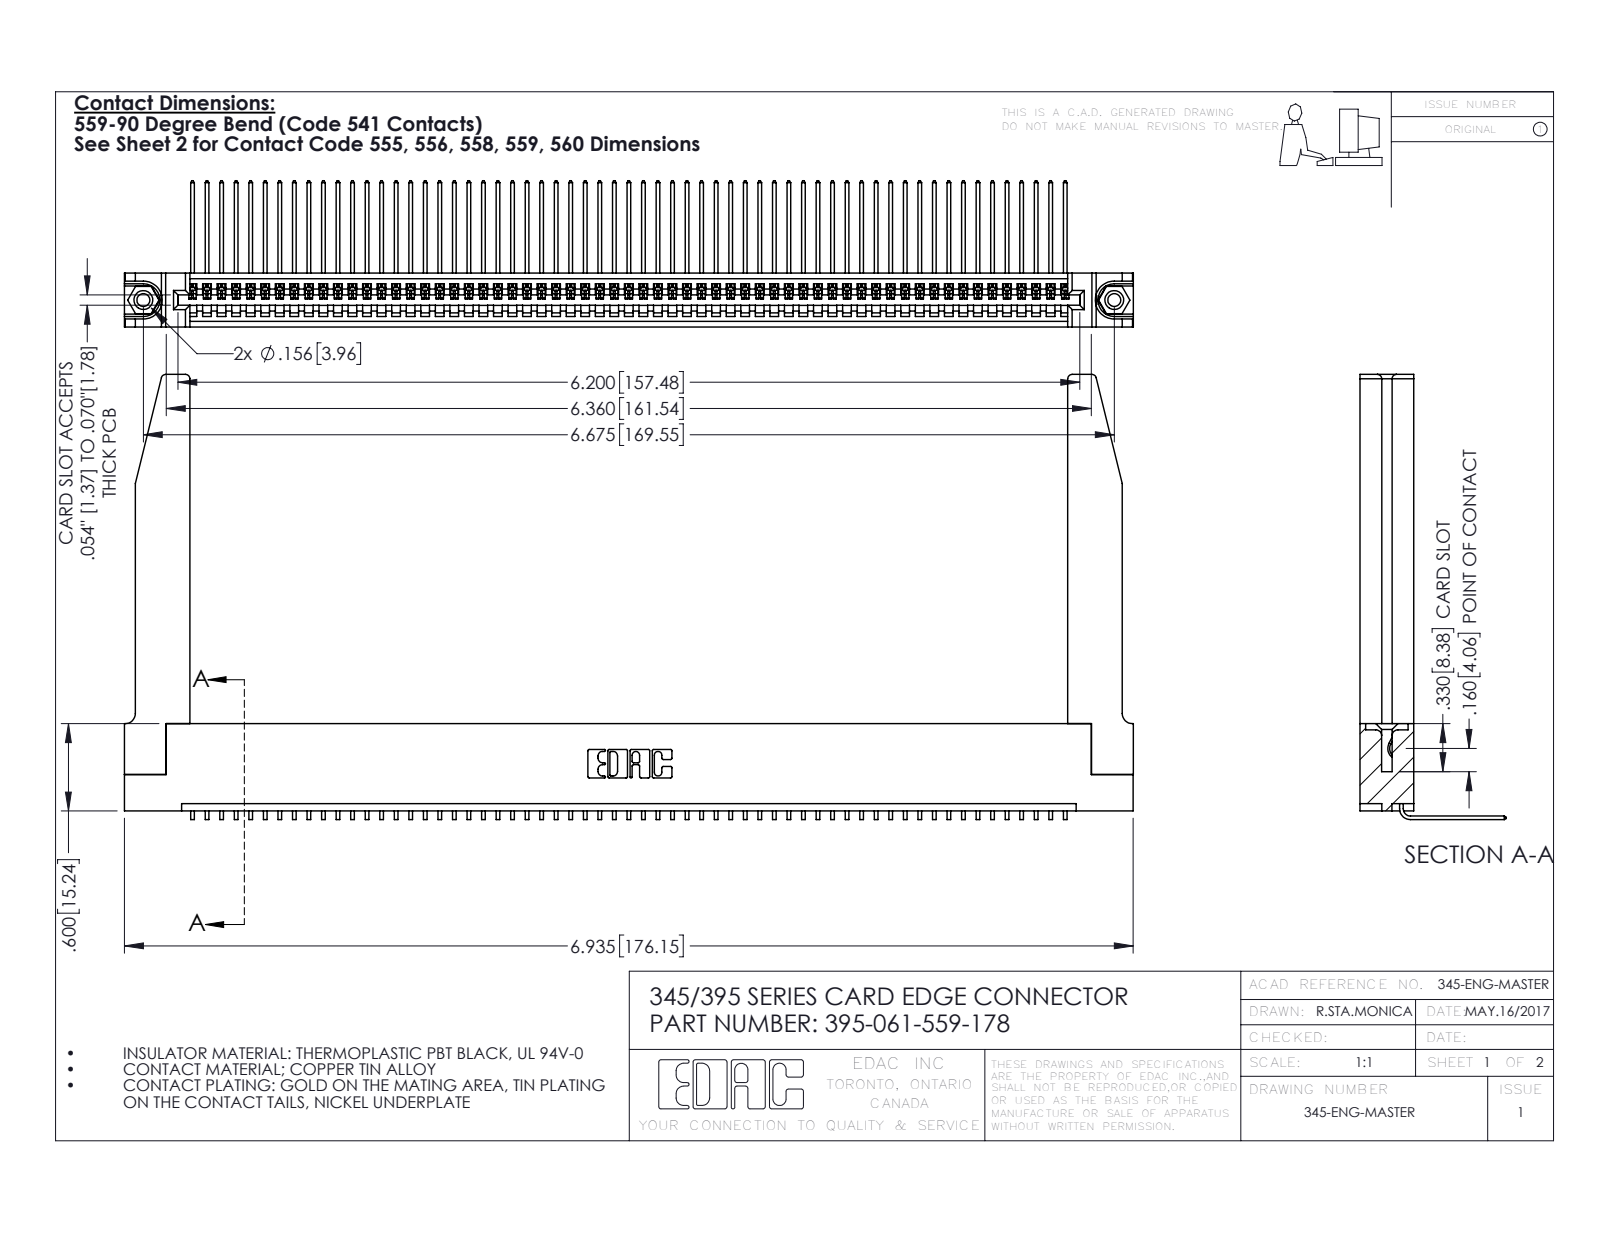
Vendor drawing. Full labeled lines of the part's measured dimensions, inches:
Part name (STEP PRODUCT): 395-061-559-178; 345-220-078_345-220-078; 345-292-001_558 559 Tail - 1; 345 Part_Flush Mounting Lugs - 0.156 Dia-TH (+1 more)
STEP written by: SolidWorks 2016 (CONFIG_CONTROL_DESIGN)
Units: inches
Bodies: 66 solids, 4020 faces (2784 planar, 1184 cylindrical, 52 other)
Overall size (bounding box): 6.936 × 3.059 × 1.005
Volume: 1.517 in³ · Surface area: 48.07 in²
Round holes (diameter × count): ⌀0.089 ×2, ⌀0.125 ×2, ⌀0.156 ×2, ⌀0.064 ×1
Round bosses / shafts (diameter × count): ⌀0.155 ×2
Partial cylindrical surfaces — rounded edges, fillets, slot ends (radius × count): R0.006 ×122, R0.01 ×22, R0.03 ×8, R0.007 ×6, R0.031 ×6, R0.026 ×3, R0.031 ×2, R0.04 ×2
Main face-to-face distances: 0.37, 0.072, 0.298, 0.2, 0.098, 0.272, 0.025, 0.225, 0.148, 0.15
Hole centre spacings: 0.27, 6.439, 6.675
